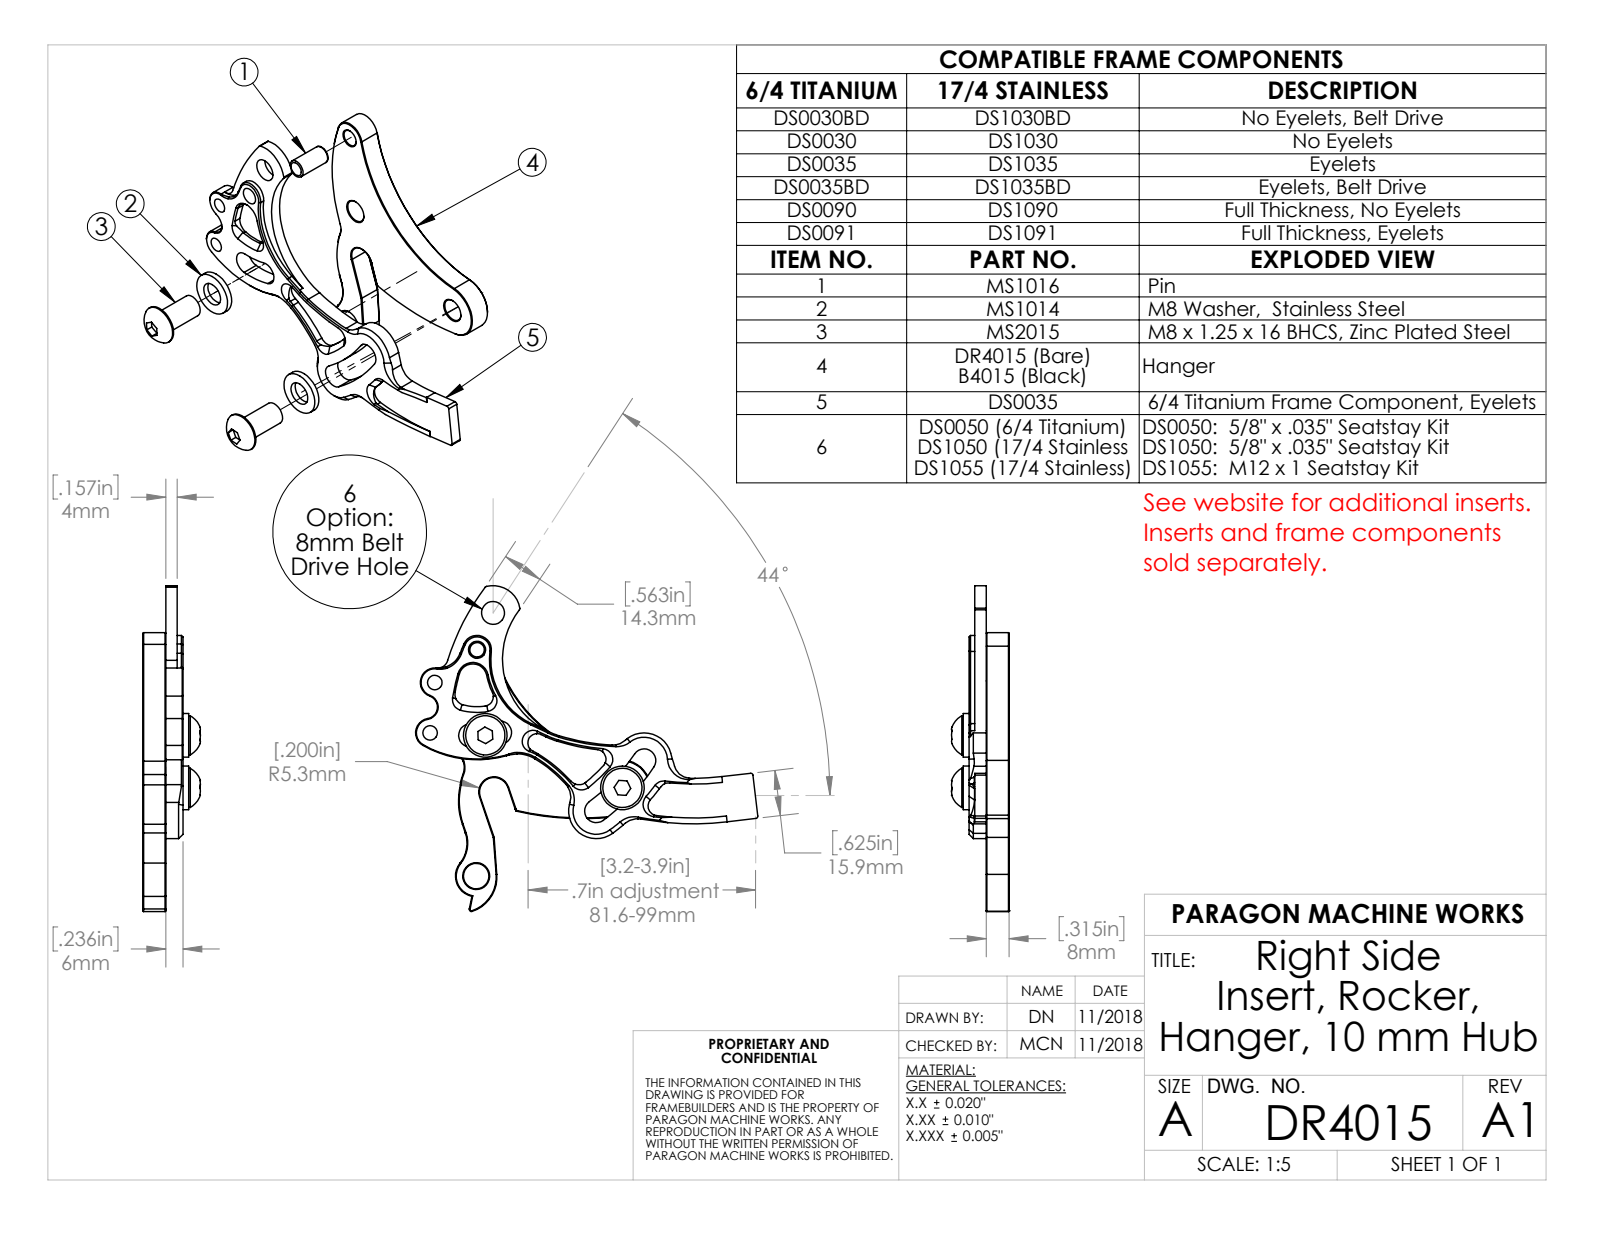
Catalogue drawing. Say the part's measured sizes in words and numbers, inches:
The part is named "DR4015". Its 3-D file was written by "SolidWorks 2018 (AUTOMOTIVE_DESIGN)". It is 1 solid with 119 faces: 11 planar, 48 cylindrical and 60 other. Overall it measures 3.832 by 2.796 by 0.315 inches. Its volume is 0.916 cubic inches and its surface area 13.33 square inches. Round holes: 1 of diameter 0.236, 1 of diameter 0.315, 1 of diameter 0.315, 1 of diameter 0.35. Partial cylindrical surfaces (rounded edges, fillets, slot ends): 12 of radius 0.01, 2 of radius 0.15, 2 of radius 0.5, 1 of radius 0.03, 1 of radius 0.1, 1 of radius 0.2, 1 of radius 0.236, 1 of radius 0.25. The main face-to-face distances are 0.315, 0.135, 0.18, 0.4, 0.355, 0.755. The hole center spacings are 1.181, 1.938, 2.019, 2.348, 2.756, 3.11.
